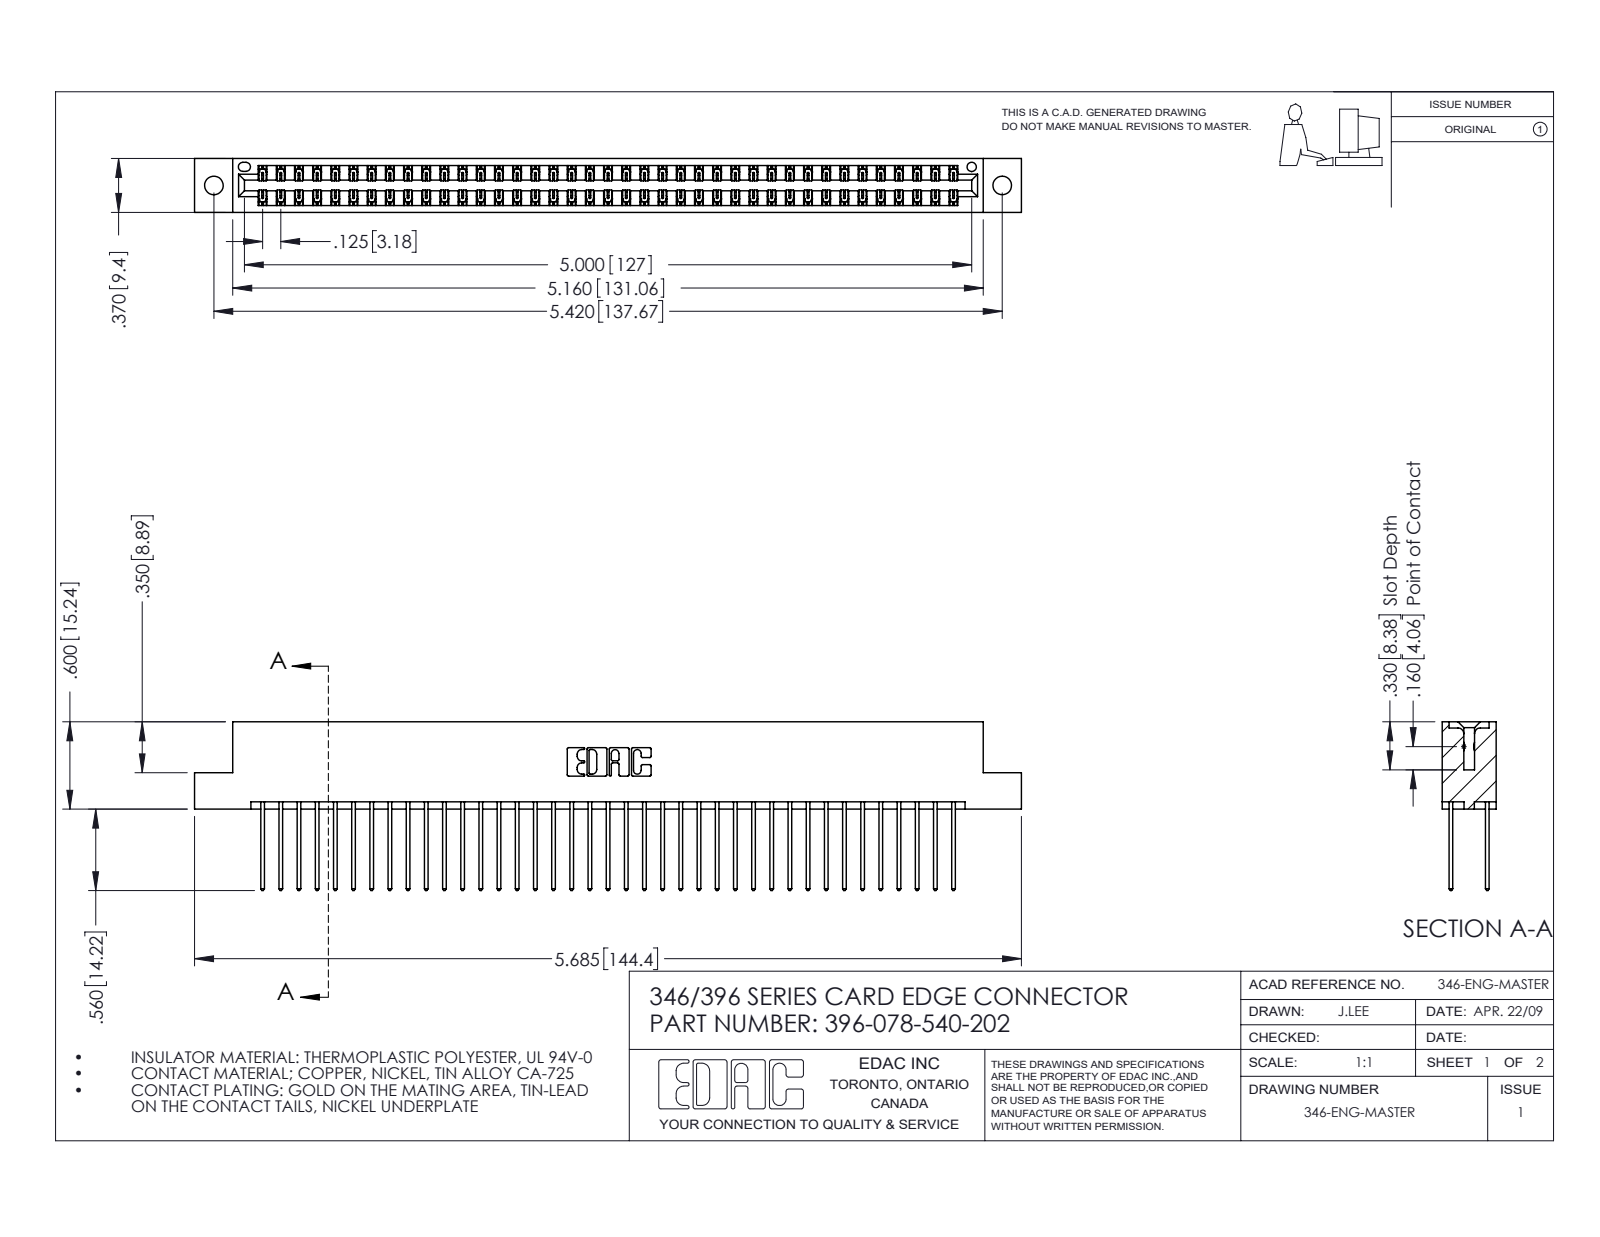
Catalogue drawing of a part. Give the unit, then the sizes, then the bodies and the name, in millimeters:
Units: millimetres
Overall size (bounding box): 144.4 × 29.5 × 9.4
Round holes (diameter × count): ⌀3.3 ×2, ⌀1.6 ×1
Partial cylindrical surfaces — rounded edges, fillets, slot ends (radius × count): R0.2 ×117, R0.3 ×78, R0.3 ×22, R0.2 ×6, R0.8 ×6, R0.7 ×3, R0.4 ×2, R0.6 ×2
Main face-to-face distances: 1.2, 8.2, 6.4, 1.8, 7.6, 0.6, 9.4, 7, 3.8, 5.6
Hole centre spacings: 6.2, 132.4, 137.7
Volume: 14 300 mm³ · Surface area: 20 760 mm²
Bodies: 79 solids, 4178 faces (2806 planar, 1372 cylindrical, 0 other)
Part name (STEP PRODUCT): 346 Part_Flush Mounting Lugs - 0.128 Dia; 396-078-540-202; 345-292-001_345-293-140
STEP written by: SolidWorks 2016 (CONFIG_CONTROL_DESIGN)
